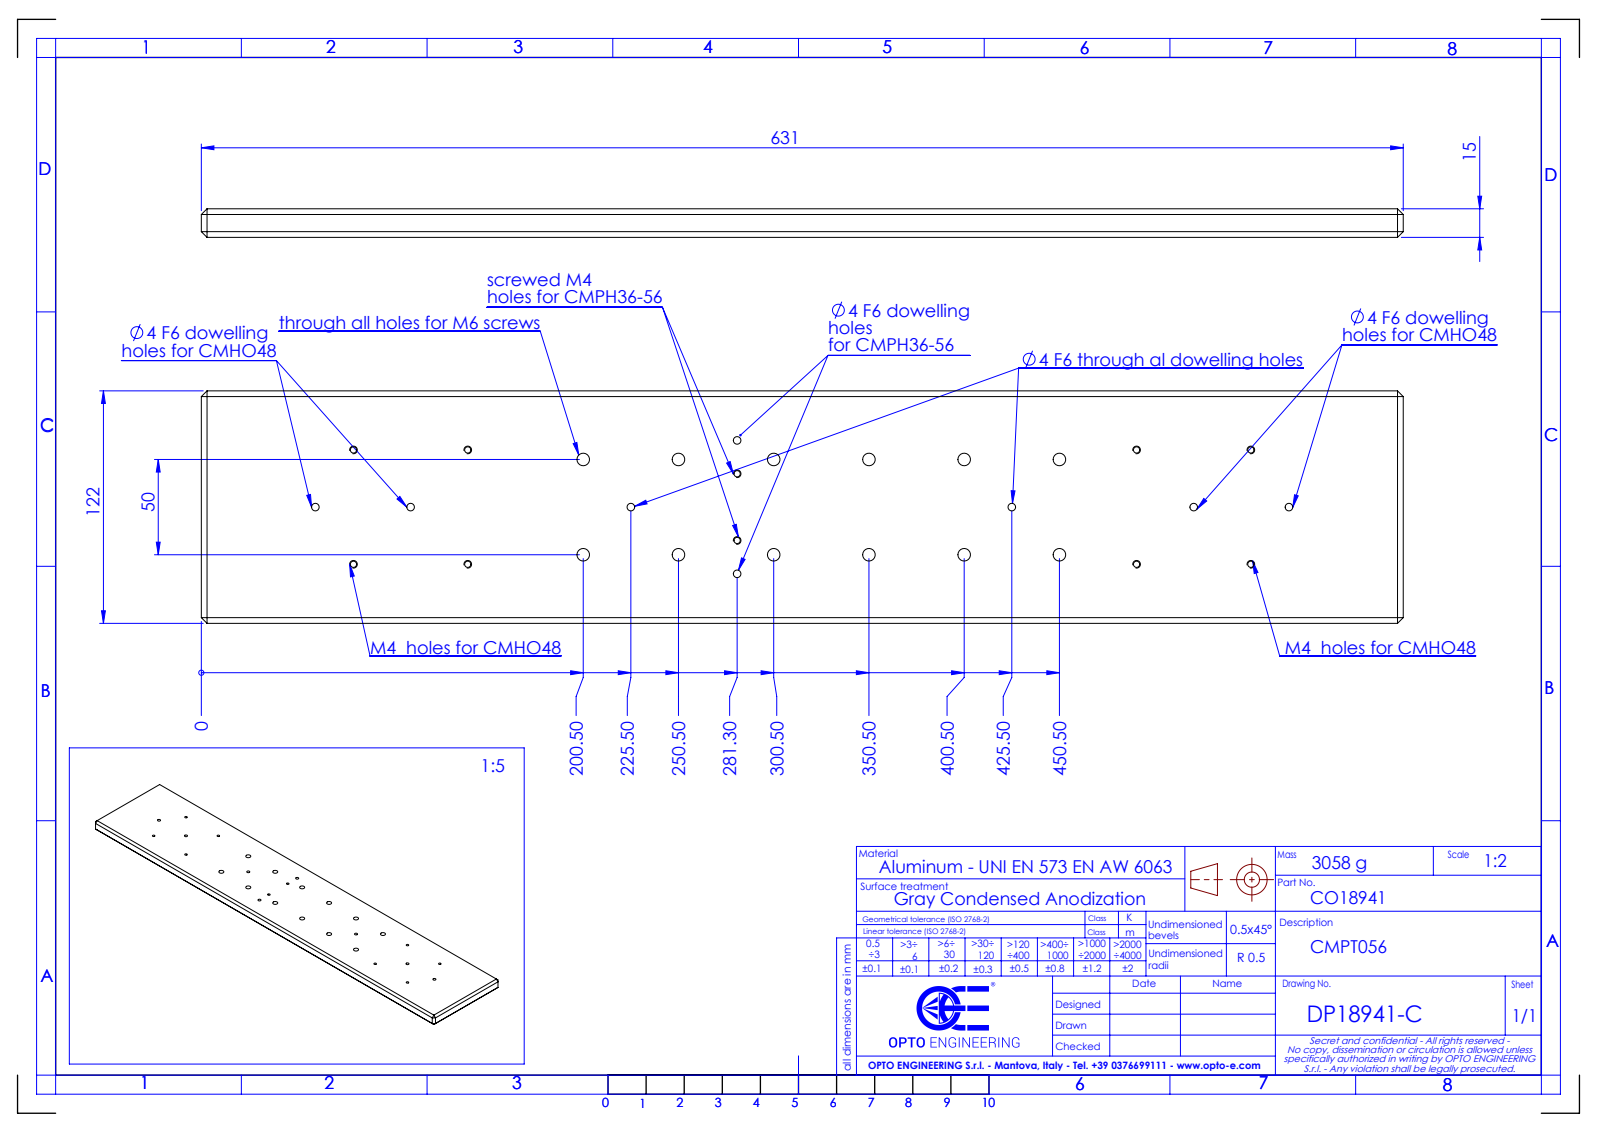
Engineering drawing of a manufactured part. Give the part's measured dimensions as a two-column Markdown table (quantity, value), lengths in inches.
| quantity | value |
| --- | --- |
| part name | DP18941-C_CMPT056 |
| STEP written by | SolidWorks 2021 (AUTOMOTIVE_DESIGN) |
| units | inches |
| bodies | 1 solid, 92 faces (32 planar, 60 cylindrical, 0 other) |
| overall size | 24.843 × 4.803 × 0.591 |
| volume | 69.14 in³ |
| surface area | 273.4 in² |
| round holes (diameter × count) | 0.26 × 12, 0.13 × 10, 0.157 × 8 |
| main face-to-face distances | 0.591, 4.803, 3.646, 24.843, 17.814, 20.793, 0.394, 0.197, 17.174, 0.217 |
| hole center spacings | 1.969, 2.784, 1.392, 1.67, 2.362, 3.937, 4.402, 5.906 |
